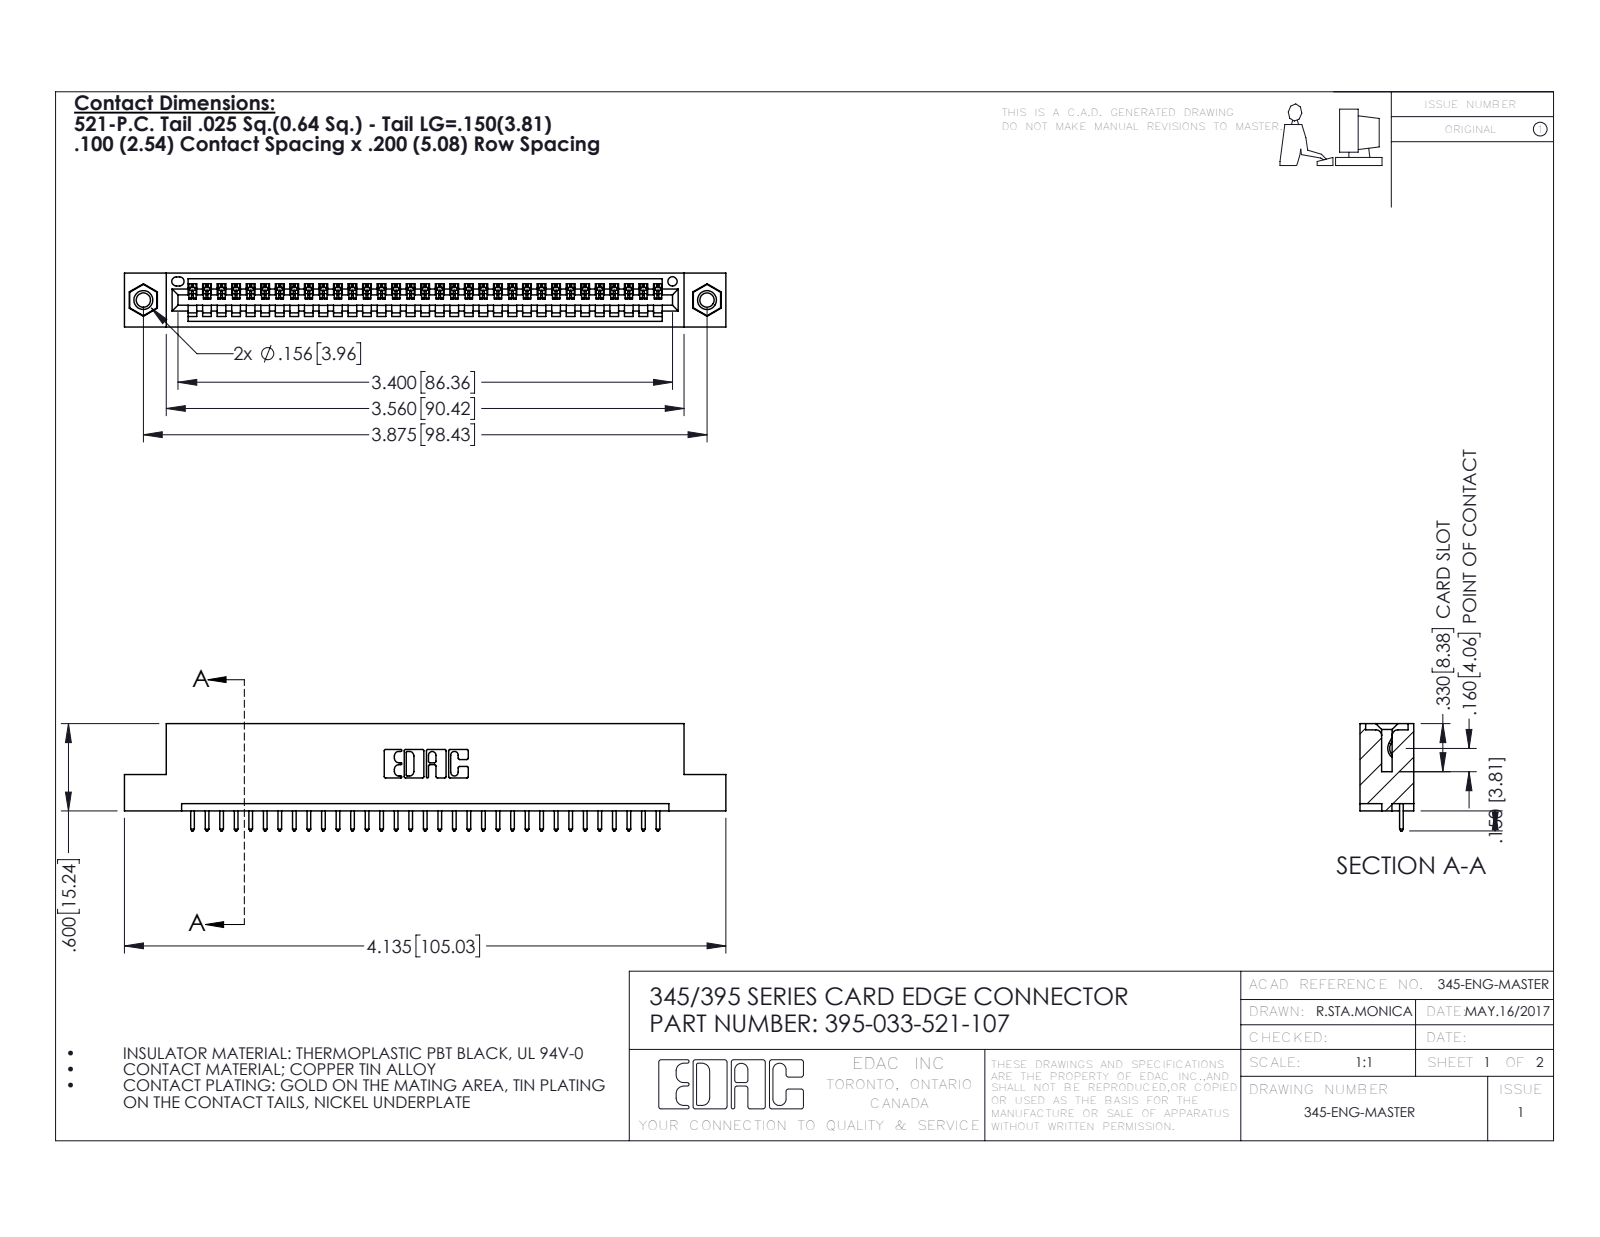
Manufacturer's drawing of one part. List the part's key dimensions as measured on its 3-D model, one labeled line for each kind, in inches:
Part name (STEP PRODUCT): 345-292-001_345-293-121; 345-250-001_345-250-005-103; 395-033-521-107; 345 Part_Flush Mounting Lugs - 0.156 Dia-TI
STEP written by: SolidWorks 2016 (CONFIG_CONTROL_DESIGN)
Units: inches
Bodies: 36 solids, 2100 faces (1432 planar, 652 cylindrical, 16 other)
Overall size (bounding box): 4.135 × 0.737 × 0.37
Volume: 0.598 in³ · Surface area: 19.47 in²
Round holes (diameter × count): ⌀0.098 ×2, ⌀0.125 ×2, ⌀0.156 ×2, ⌀0.064 ×1
Round bosses / shafts (diameter × count): ⌀0.155 ×2
Partial cylindrical surfaces — rounded edges, fillets, slot ends (radius × count): R0.006 ×66, R0.01 ×66, R0.01 ×22, R0.007 ×6, R0.031 ×6, R0.026 ×3, R0.031 ×2, R0.04 ×2
Main face-to-face distances: 0.072, 0.298, 0.2, 0.37, 0.098, 0.272, 0.025, 0.225, 0.149, 0.072
Hole centre spacings: 0.27, 3.64, 3.875
